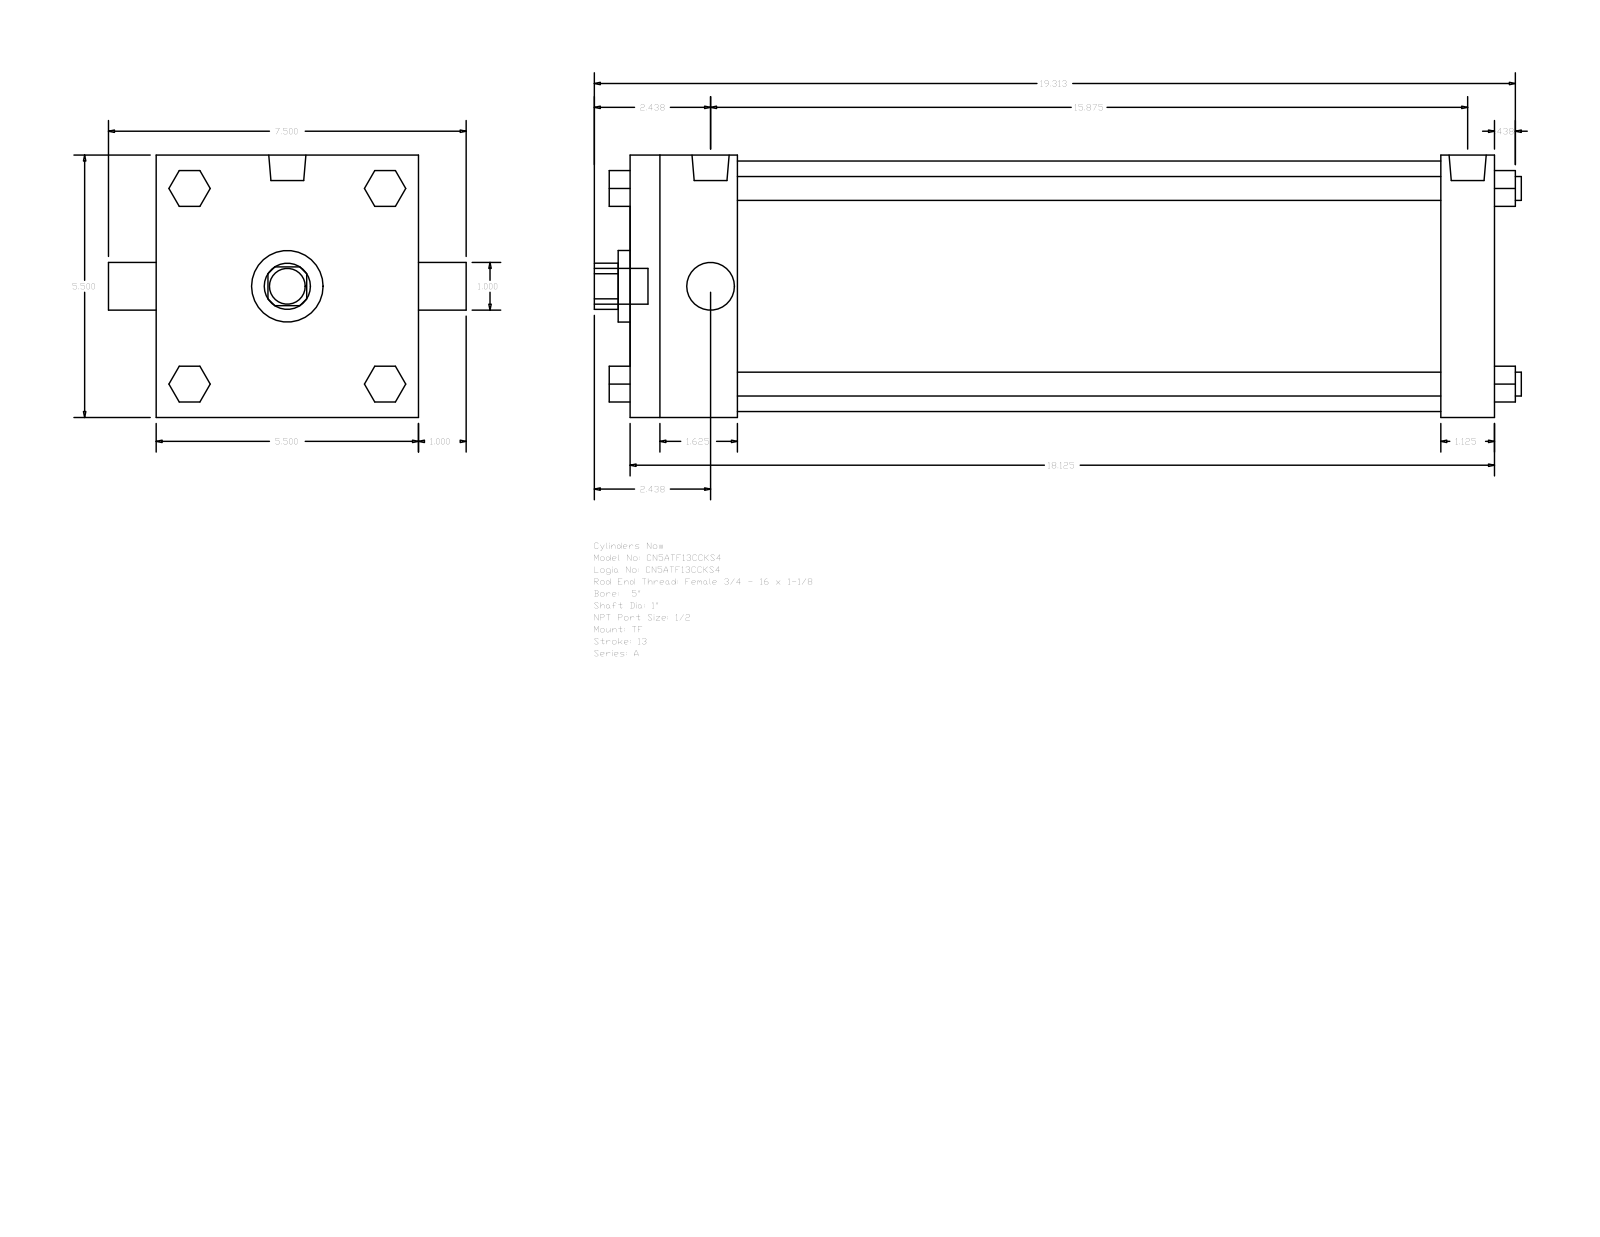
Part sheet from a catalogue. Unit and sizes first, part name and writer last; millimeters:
Units: millimetres
Overall size (bounding box): 493.71 × 190.5 × 139.7
Round holes (diameter × count): ⌀25.4 ×2, ⌀38.1 ×1, ⌀133.35 ×1
Round bosses / shafts (diameter × count): ⌀12.7 ×4, ⌀8.73 ×3, ⌀19.77 ×2, ⌀19.05 ×1
Partial cylindrical surfaces — rounded edges, fillets, slot ends (radius × count): R12.29 ×1
Main face-to-face distances: 139.7, 460.38, 431.8, 28.58, 57.15, 374.65, 403.23, 19.05, 52.07, 90.18
Bodies: 0 solids, 120 faces (92 planar, 28 cylindrical, 0 other)
Part name (STEP PRODUCT): A_TF__0500_1
STEP written by: GSSL Pune (CONFIG_CONTROL_DESIGN)
